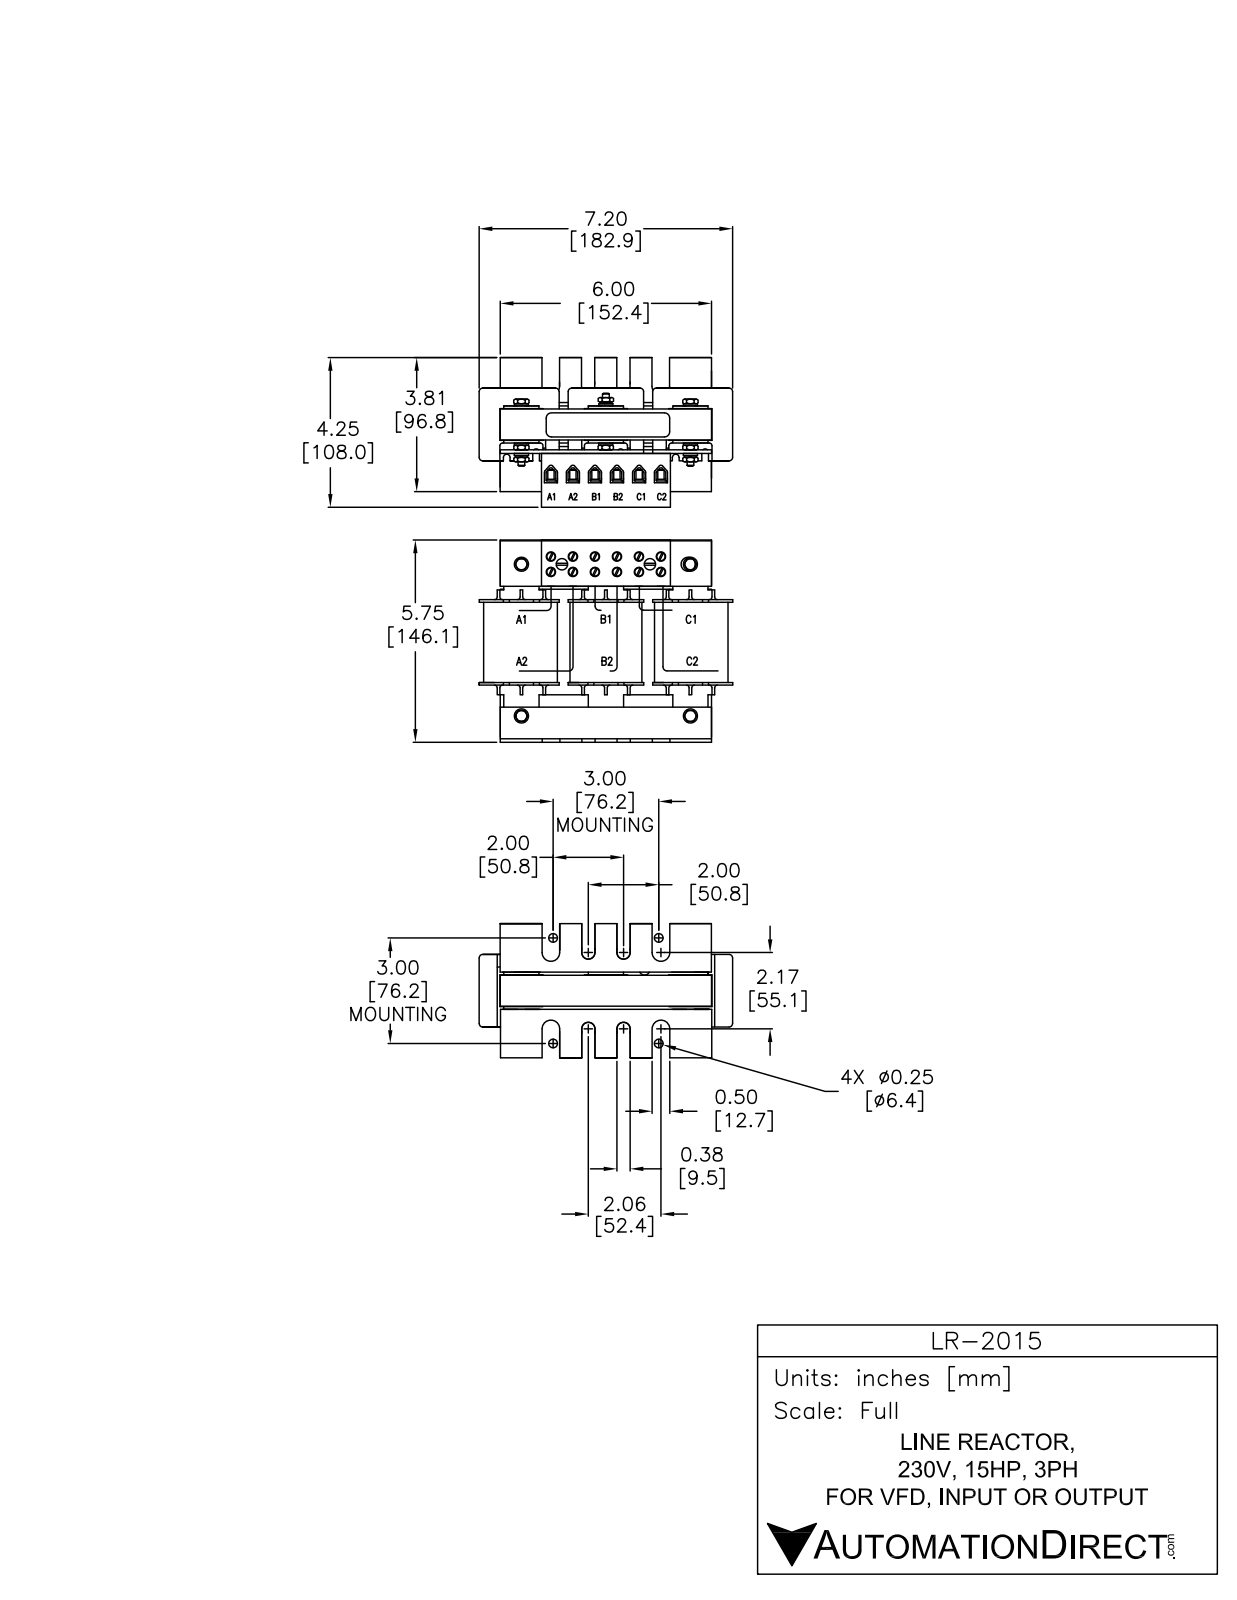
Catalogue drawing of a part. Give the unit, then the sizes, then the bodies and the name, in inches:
Units: inches
Overall size (bounding box): 7.008 × 5.619 × 3.907
Round holes (diameter × count): ⌀0.276 ×12, ⌀0.305 ×5
Round bosses / shafts (diameter × count): ⌀0.472 ×5, ⌀0.413 ×5, ⌀0.305 ×2, ⌀0.183 ×2, ⌀0.184 ×1, ⌀0.183 ×1, ⌀0.183 ×1
Partial cylindrical surfaces — rounded edges, fillets, slot ends (radius × count): R0.106 ×24, R0.197 ×12, R0.276 ×12, R0.089 ×6, R0.059 ×4, R0.177 ×4, R0.246 ×4, R0.128 ×2
Main face-to-face distances: 0.079, 0.364, 2.441, 1.329, 1.407, 0.108, 0.344, 0.266, 0.443, 0.187
Hole centre spacings: 0.63, 1.26, 0.376, 0.394, 0.77, 0.96, 0.981, 1.335
Volume: 51.71 in³ · Surface area: 302.9 in²
Bodies: 34 solids, 1041 faces (767 planar, 242 cylindrical, 32 other)
Part name (STEP PRODUCT): LR-2015
STEP written by: SolidWorks 2011 (AUTOMOTIVE_DESIGN)
